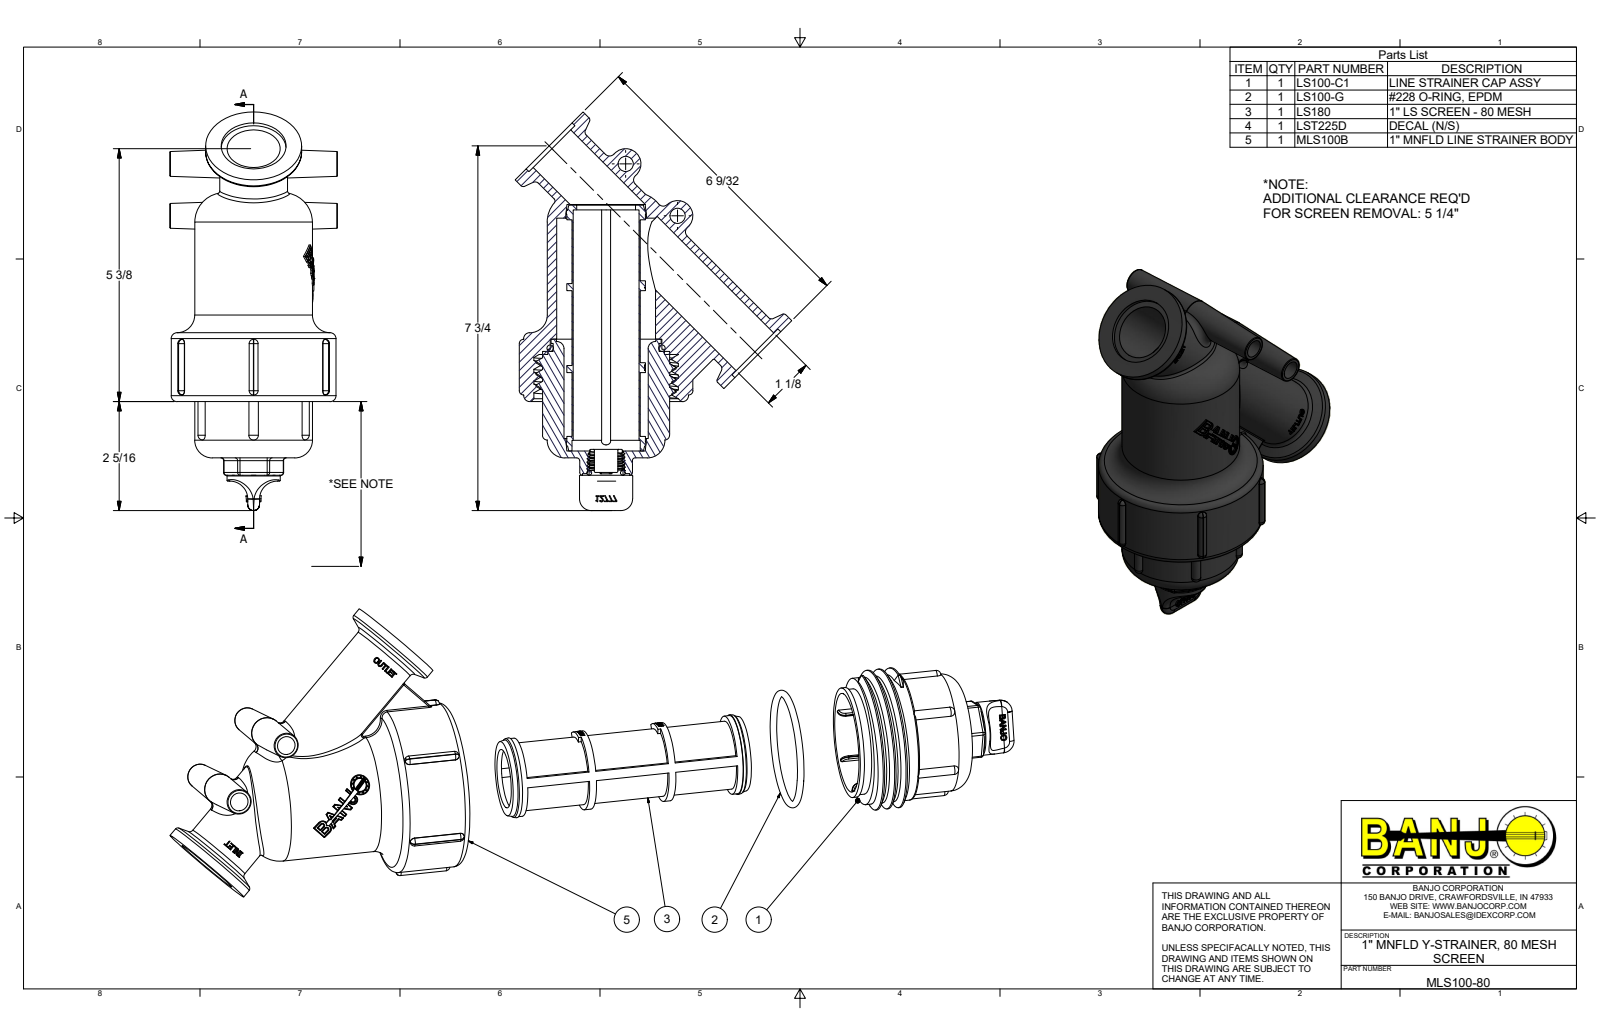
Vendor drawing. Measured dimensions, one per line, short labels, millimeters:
name: MLS100B; LS100XC1; 12777; UV15163 (+4 more)
written by: Autodesk Inventor 2015 (AUTOMOTIVE_DESIGN)
unit: mm
bodies: 6 solids, 1210 faces (612 planar, 259 cylindrical, 339 other)
size: 215.01 × 149.25 × 90.49
volume: 364 264 mm³; area: 172 984 mm²
holes: 2× ⌀28.7, 2× ⌀35.05, 1× ⌀6.92, 1× ⌀9.77, 1× ⌀12.7, 1× ⌀25.53, 1× ⌀31.75, 1× ⌀35.56, 1× ⌀53.34, 1× ⌀53.59, 1× ⌀60.22, 1× ⌀62.99
bosses: 2× ⌀51.82, 1× ⌀88.9, 1× ⌀75.45, 1× ⌀68.58, 1× ⌀63.5, 1× ⌀59.44, 1× ⌀57.15, 1× ⌀42.42
rounds: 39× R2.29, 27× R0.76, 18× R1.52, 9× R2.54, 6× R3.81, 2× R0.99, 2× R1.25, 2× R2.41
face distances: 1.65, 52.07, 8.25, 159.23, 60.32, 6.6, 53.72, 125.6, 73.53, 71.88
